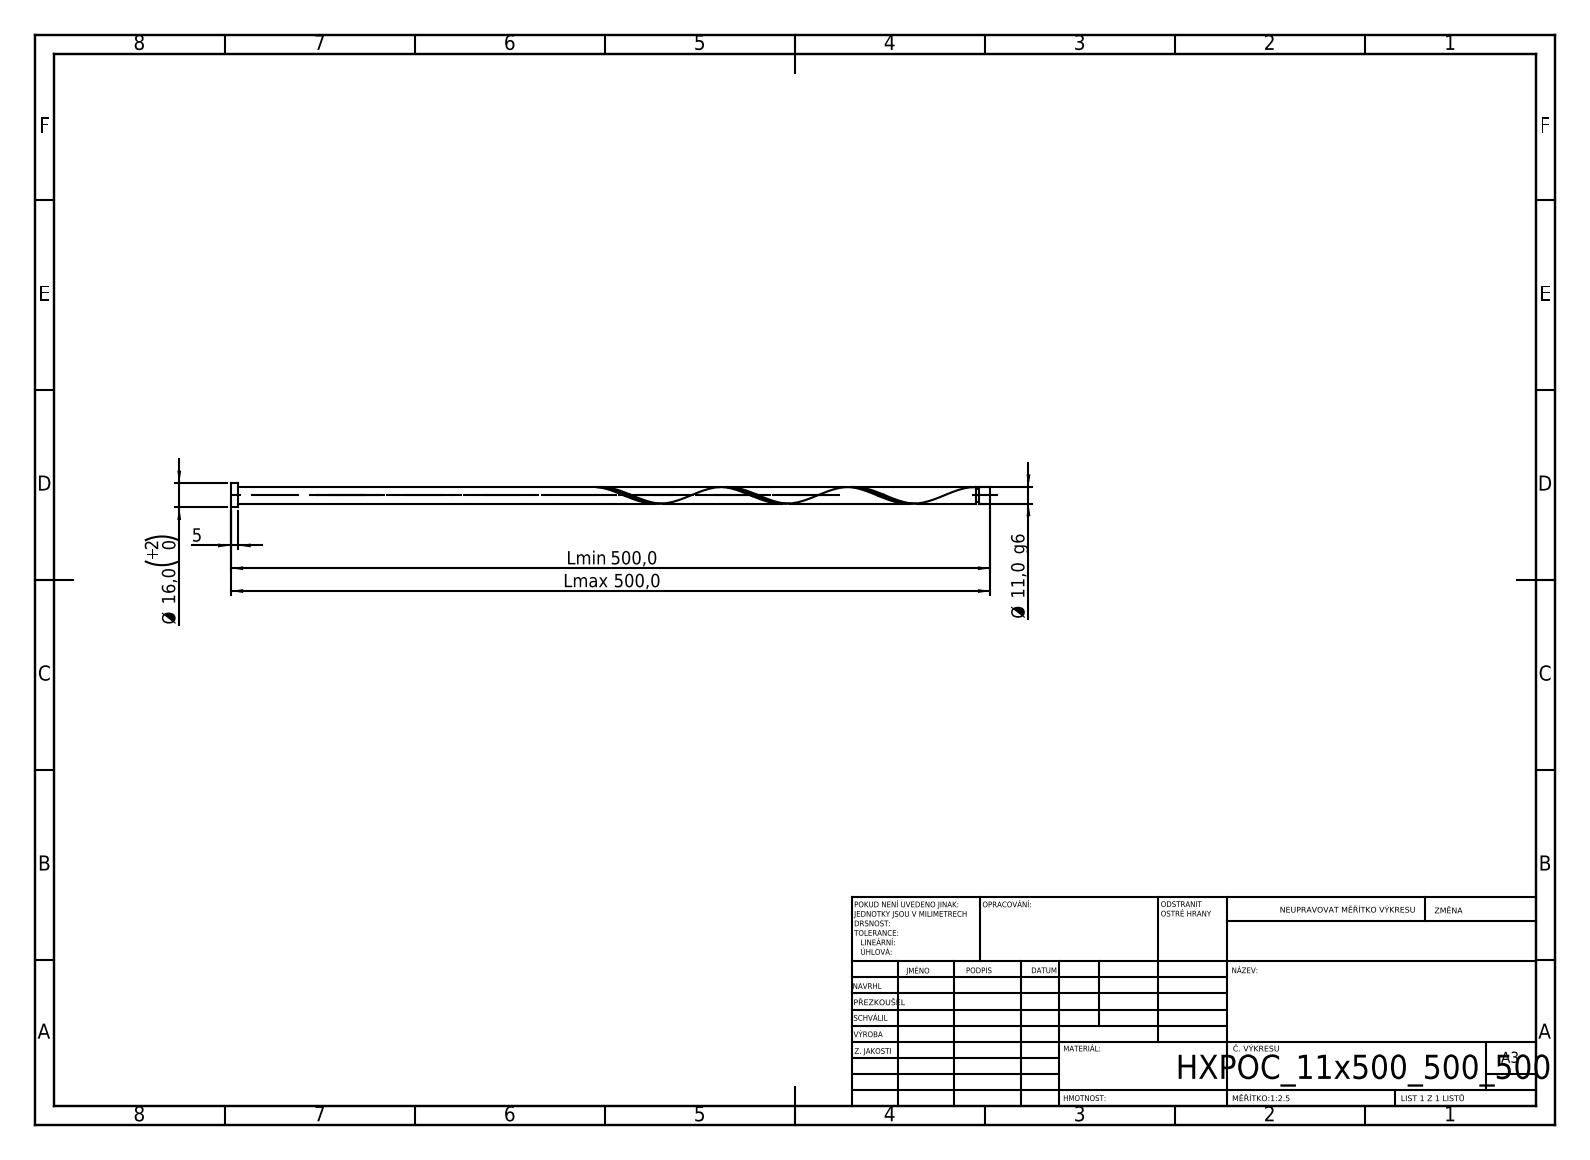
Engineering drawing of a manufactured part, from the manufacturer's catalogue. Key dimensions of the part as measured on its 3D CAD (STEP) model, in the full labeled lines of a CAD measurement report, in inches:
STEP written by: SolidWorks 2019 (CONFIG_CONTROL_DESIGN)
Units: inches
Bodies: 1 solid, 21 faces (6 planar, 14 cylindrical, 1 other)
Overall size (bounding box): 19.685 × 0.63 × 0.63
Volume: 2.9 in³ · Surface area: 28.06 in²
Round bosses / shafts (diameter × count): ⌀0.63 ×1, ⌀0.433 ×1, ⌀0.346 ×1
Main face-to-face distances: 0.197, 19.685, 19.488, 19.398, 19.201, 0.287, 19.311, 19.115, 0.087, 0.374
